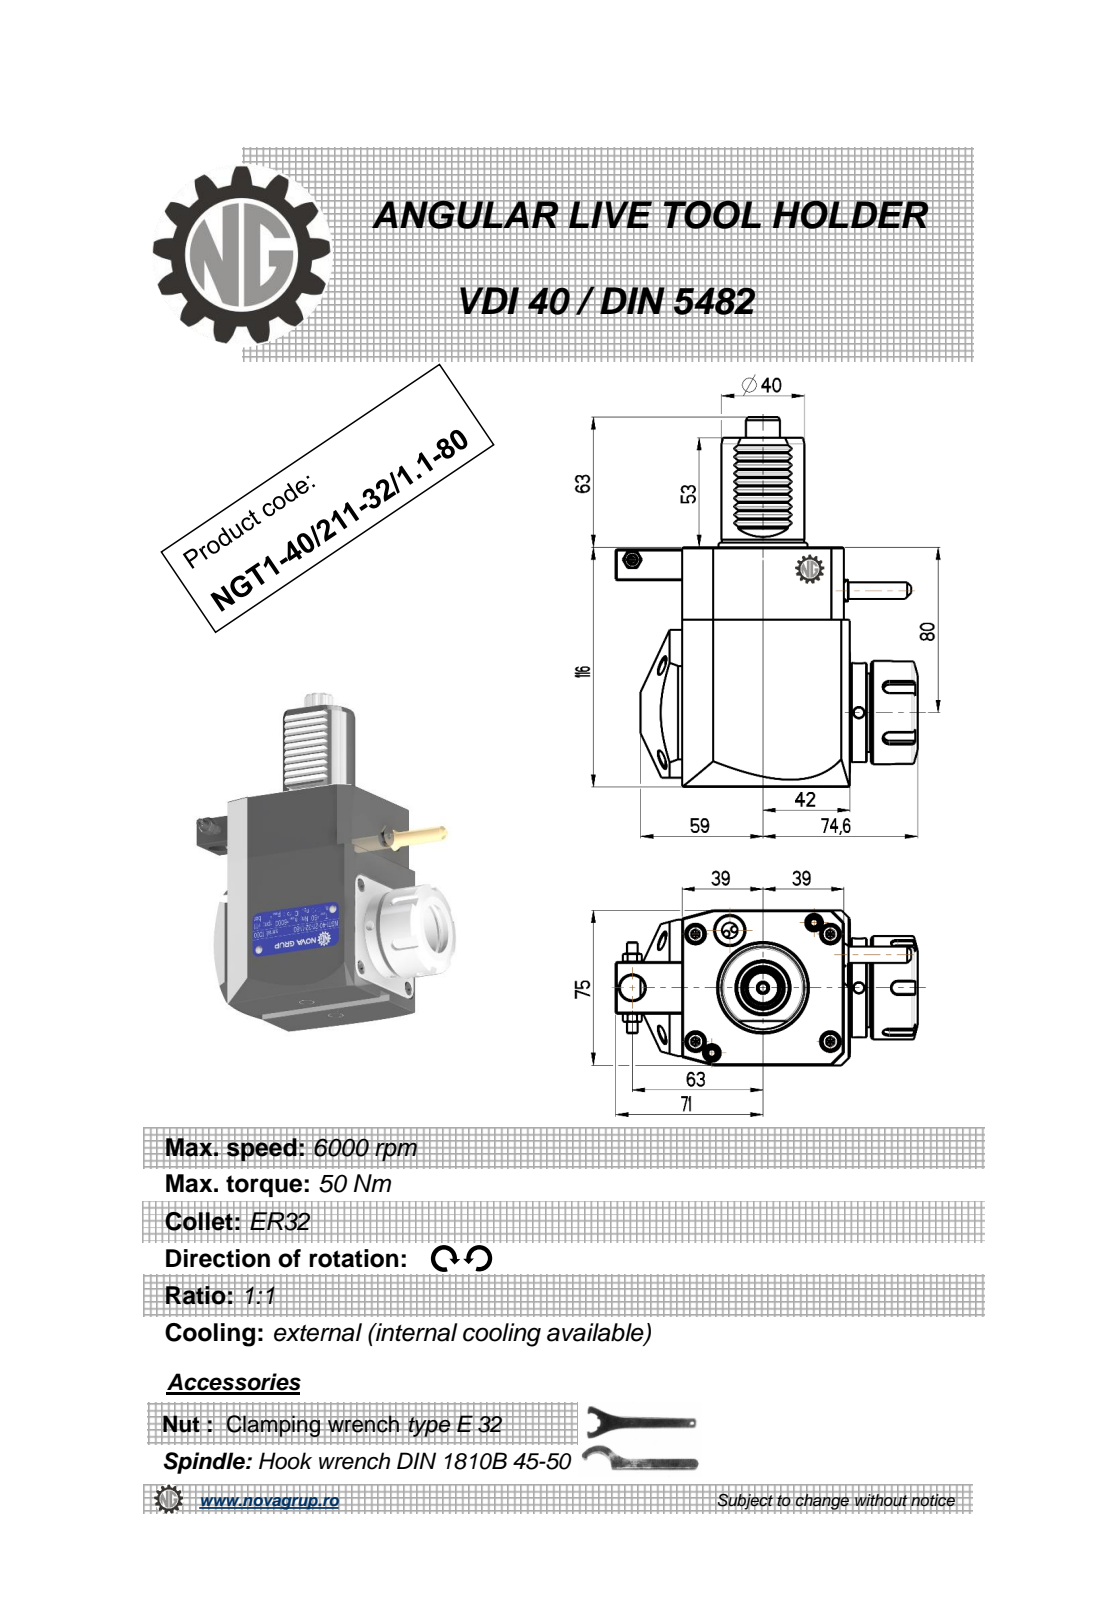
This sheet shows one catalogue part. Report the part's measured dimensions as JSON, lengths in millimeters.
{"part_name": "NGT1_40_211_32_1_1_80", "step_written_by": "PRO/ENGINEER BY PARAMETRIC TECHNOLOGY CORPORATION, 2010280 (CONFIG_CONTROL_DESIGN)", "units": "millimeters", "bodies": {"solids": 1, "faces": 457, "planar": 189, "cylindrical": 124, "other": 144}, "overall_size": [179, 145.6, 76.6], "volume_mm3": 868760, "surface_area_mm2": 69575, "round_holes": [[5, 3], [4.2, 2], [3, 1], [9.5, 1], [12, 1], [27, 1]], "round_bosses_or_shafts": [[50, 1], [48, 1], [41, 1], [40, 1], [11.2, 1], [8.96, 1], [8, 1], [5, 1]], "partial_cylinders_radius": [[3.03, 18], [0.26, 12], [0.3, 10], [0.22, 6], [3, 5], [0.5, 1], [6.75, 1], [8.22, 1]], "face_to_face_distances": [75, 116, 81, 3, 78, 80.8, 2.8, 25, 4.5, 7.5], "hole_center_spacings": [20.93, 46.25, 61.13, 63, 72.5, 109.25, 131.95]}
